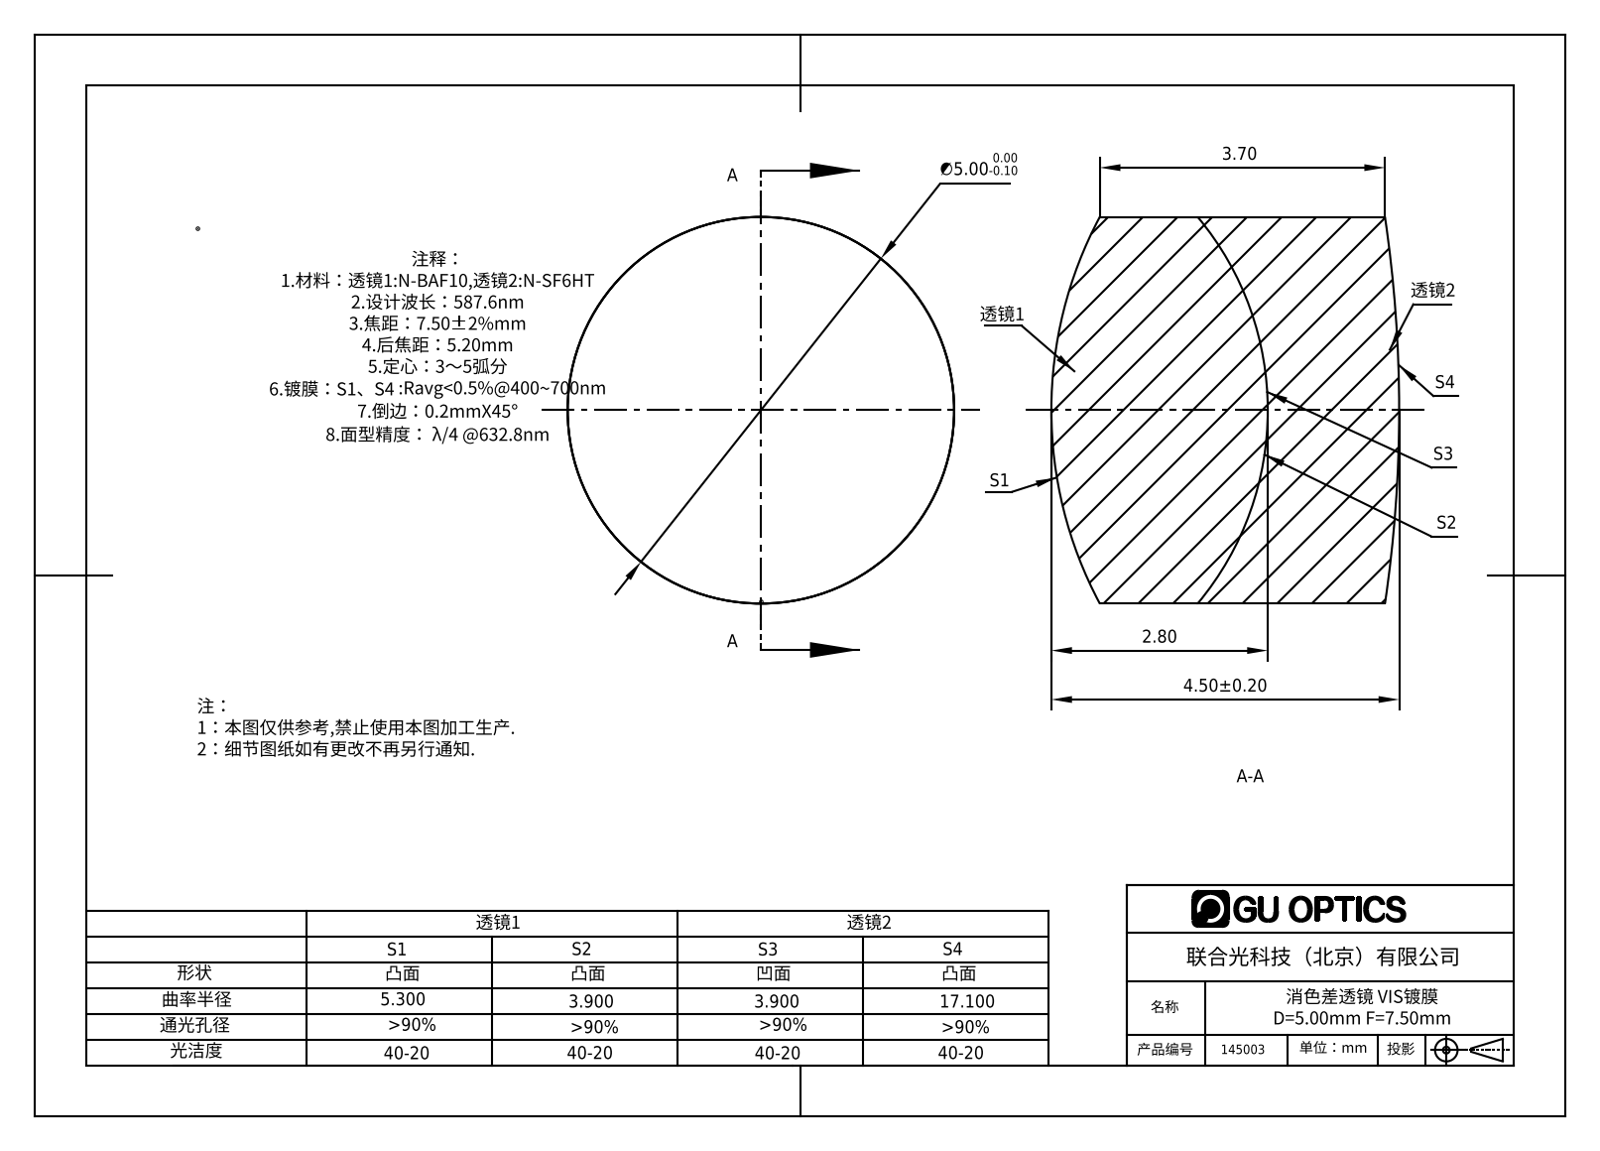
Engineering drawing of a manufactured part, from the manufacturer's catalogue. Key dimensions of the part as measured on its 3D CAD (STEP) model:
Part name (STEP PRODUCT): 145003
STEP written by: SolidWorks 2016 (AUTOMOTIVE_DESIGN)
Units: millimetres
Bodies: 2 solids, 12 faces (0 planar, 4 cylindrical, 8 other)
Overall size (bounding box): 5 × 5 × 4.5
Volume: 81 mm³ · Surface area: 143 mm²
Round bosses / shafts (diameter × count): ⌀5 ×1
